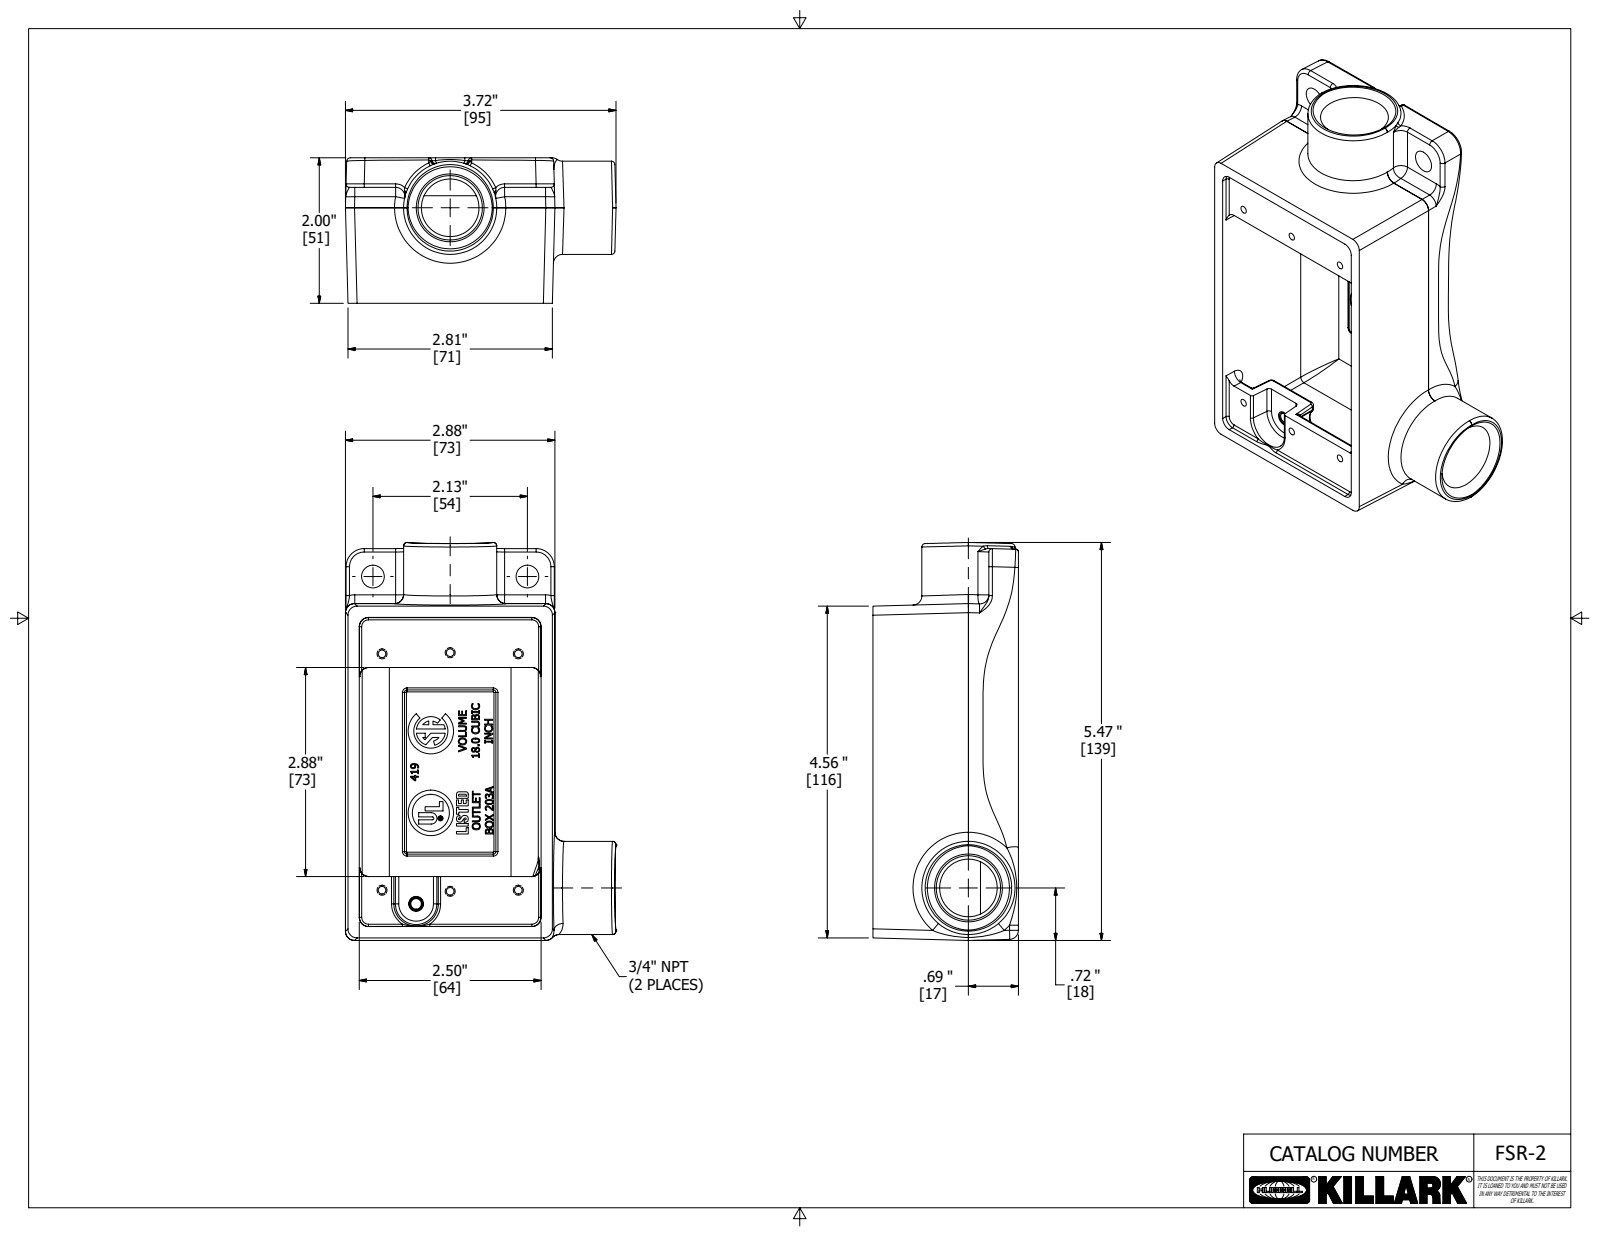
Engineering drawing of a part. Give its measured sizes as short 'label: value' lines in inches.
name: 23859-3
written by: Autodesk Inventor 2020 (AUTOMOTIVE_DESIGN)
unit: in
bodies: 1 solid, 1139 faces (568 planar, 158 cylindrical, 413 other)
size: 5.472 × 3.722 × 2.075
volume: 9.761 in³; area: 95.45 in²
holes: 6× ⌀0.104, 2× ⌀0.595, 1× ⌀0.069, 1× ⌀0.145, 1× ⌀0.625
bosses: 1× ⌀1.281, 1× ⌀0.509, 1× ⌀0.058
rounds: 38× R0.031, 14× R0.047, 11× R0.125, 7× R0.094, 5× R0.062, 4× R0.375, 2× R0.013, 2× R0.014
face distances: 2.656, 0.156, 4.406, 1.75, 0.225, 0.031, 1.719, 1.906, 1.594, 0.25
hole spacings: 0.937, 3.397, 1.875, 3.25, 3.752, 0.153, 0.5, 0.505
